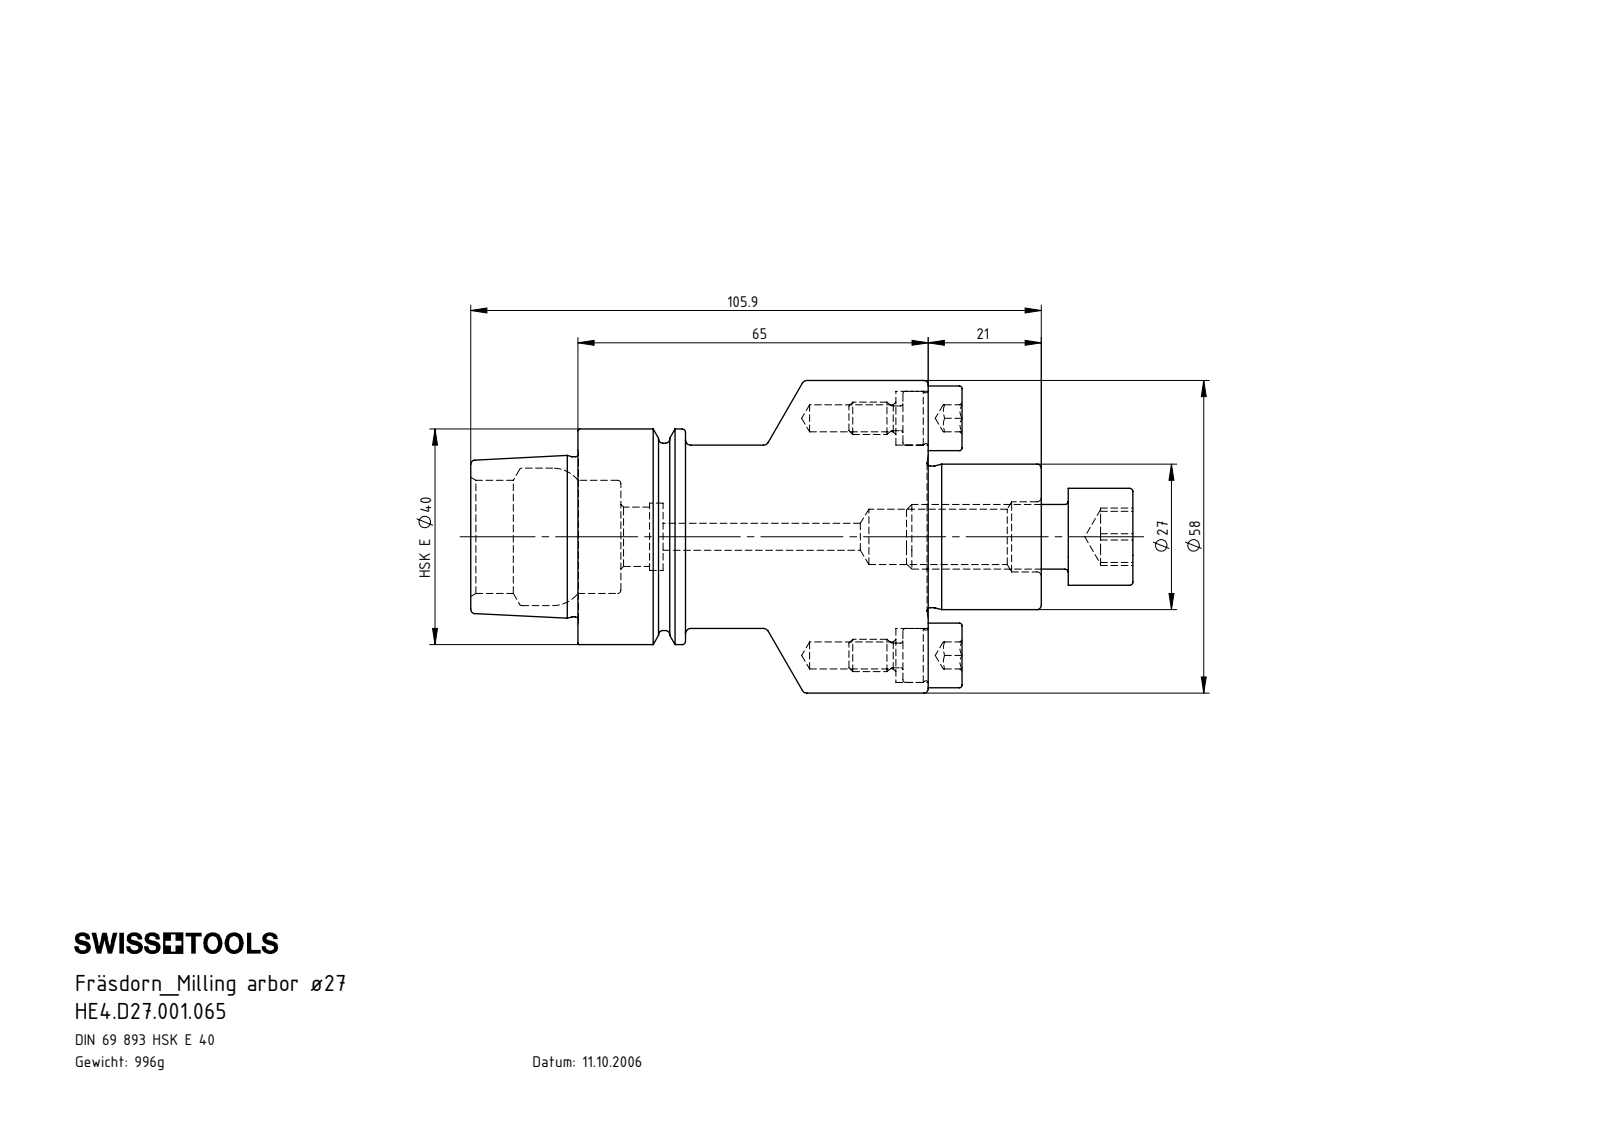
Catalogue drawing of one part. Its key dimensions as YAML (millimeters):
part_name: "D27-ER2.001.021_B; HE4-D27.001.065_A_Fertigbearbeitung; HE4.D27.001.065; D27-ER1.002.030_A"
step_written_by: "SolidWorks 2017 (CONFIG_CONTROL_DESIGN)"
units: millimeters
bodies: {solids: 4, faces: 229, planar: 47, cylindrical: 60, other: 122}
overall_size: [122.9, 58, 58]
volume: 126899
surface_area: 27277
round_holes:
  - {diameter: 5, count: 3}
  - {diameter: 10, count: 2}
  - {diameter: 10.25, count: 1}
  - {diameter: 11, count: 1}
  - {diameter: 12.5, count: 1}
  - {diameter: 13, count: 1}
  - {diameter: 21, count: 1}
  - {diameter: 25.5, count: 1}
round_bosses_or_shafts:
  - {diameter: 12, count: 3}
  - {diameter: 6, count: 2}
  - {diameter: 4.6, count: 2}
  - {diameter: 58, count: 1}
  - {diameter: 40, count: 1}
  - {diameter: 34.75, count: 1}
  - {diameter: 34, count: 1}
  - {diameter: 29.71, count: 1}
face_to_face_distances: [65, 21, 86, 12, 83.05, 7.95, 57.05, 78.05, 19.9, 27.85]
hole_center_spacings: [22, 44]
